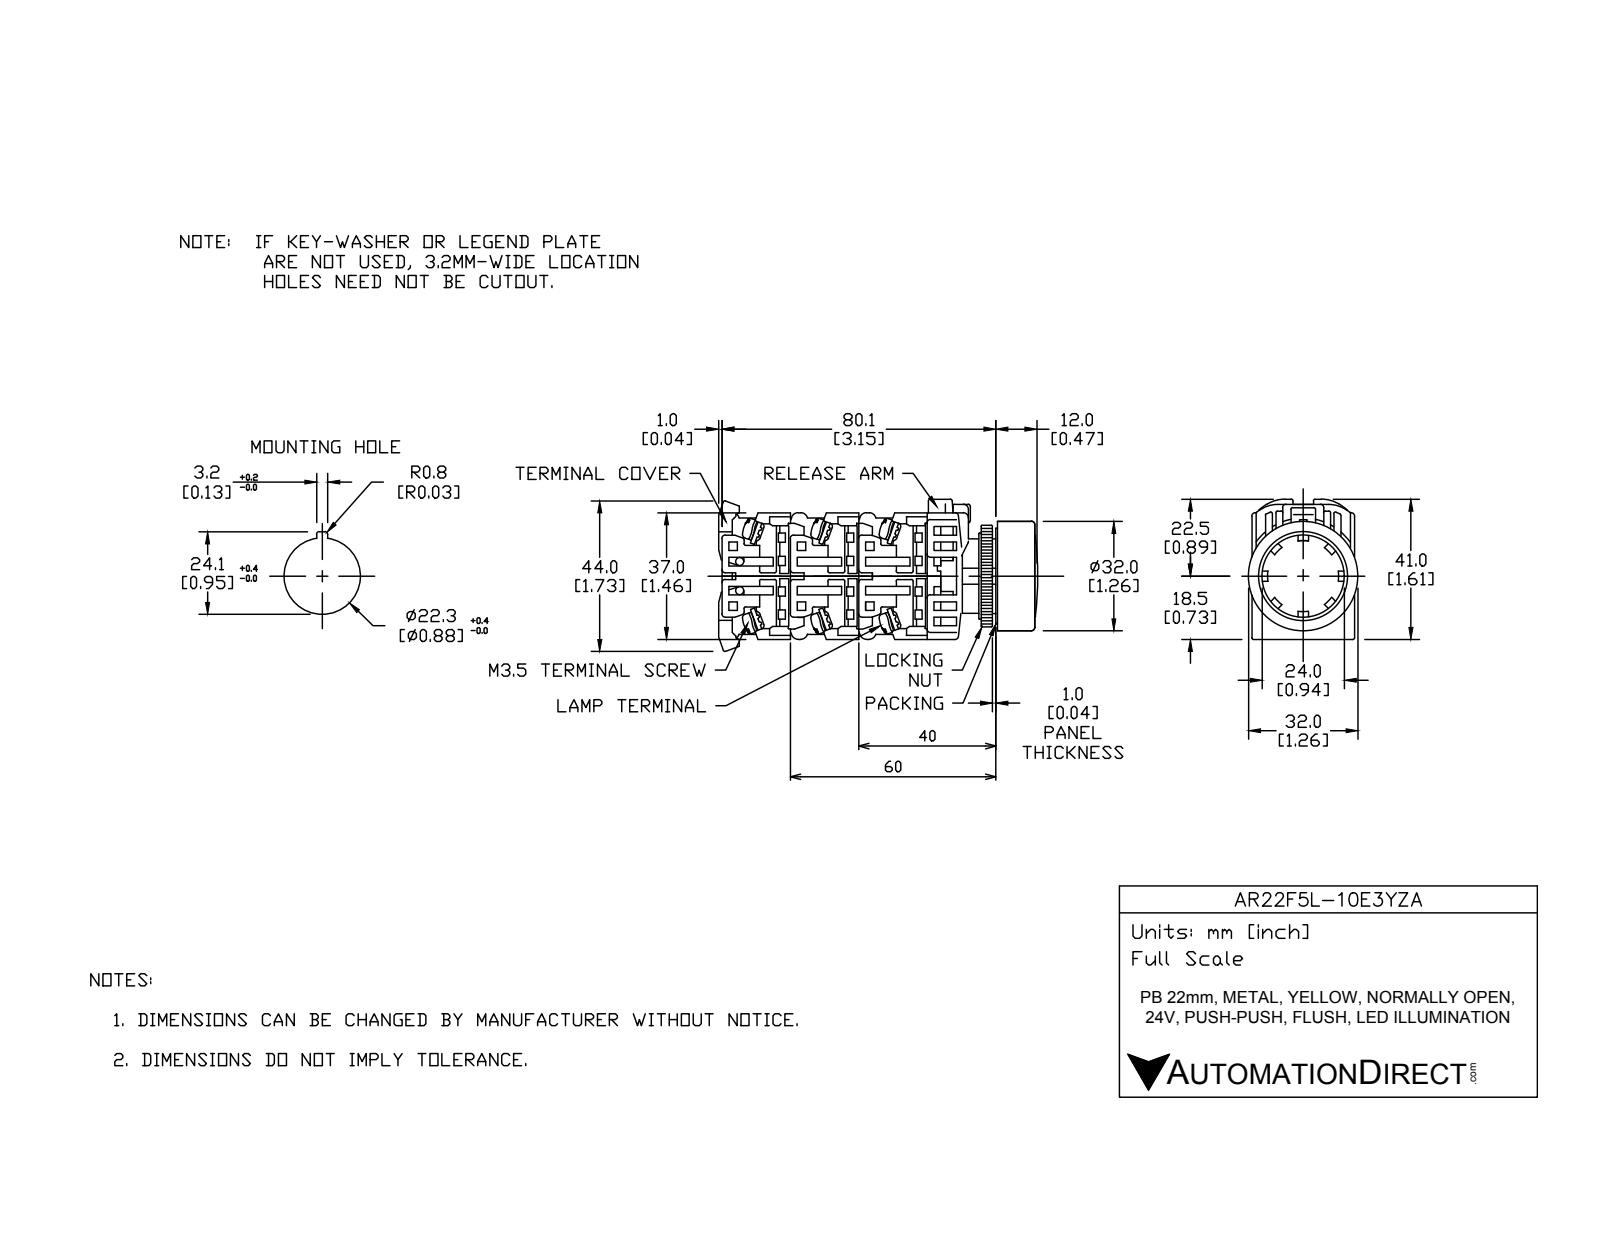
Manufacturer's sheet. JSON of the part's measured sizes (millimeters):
{"part_name": "AR22F5L-10E3YZA", "step_written_by": "SolidWorks 2017 (AUTOMOTIVE_DESIGN)", "units": "millimeters", "bodies": {"solids": 18, "faces": 475, "planar": 329, "cylindrical": 111, "other": 35}, "overall_size": [52.75, 43.81, 32], "volume_mm3": 36367, "surface_area_mm2": 24064, "round_holes": [[21.8, 1], [22, 1], [25, 1], [31, 1]], "round_bosses_or_shafts": [[5, 4], [32, 1], [30.5, 1], [29.8, 1], [24, 1], [23.8, 1], [21.75, 1], [17, 1]], "partial_cylinders_radius": [[0.5, 39], [1.75, 8], [5, 4], [4, 2], [16.59, 1], [17.59, 1]], "face_to_face_distances": [1, 18, 28.5, 48.5, 20, 29, 3, 2, 21, 0.5]}
